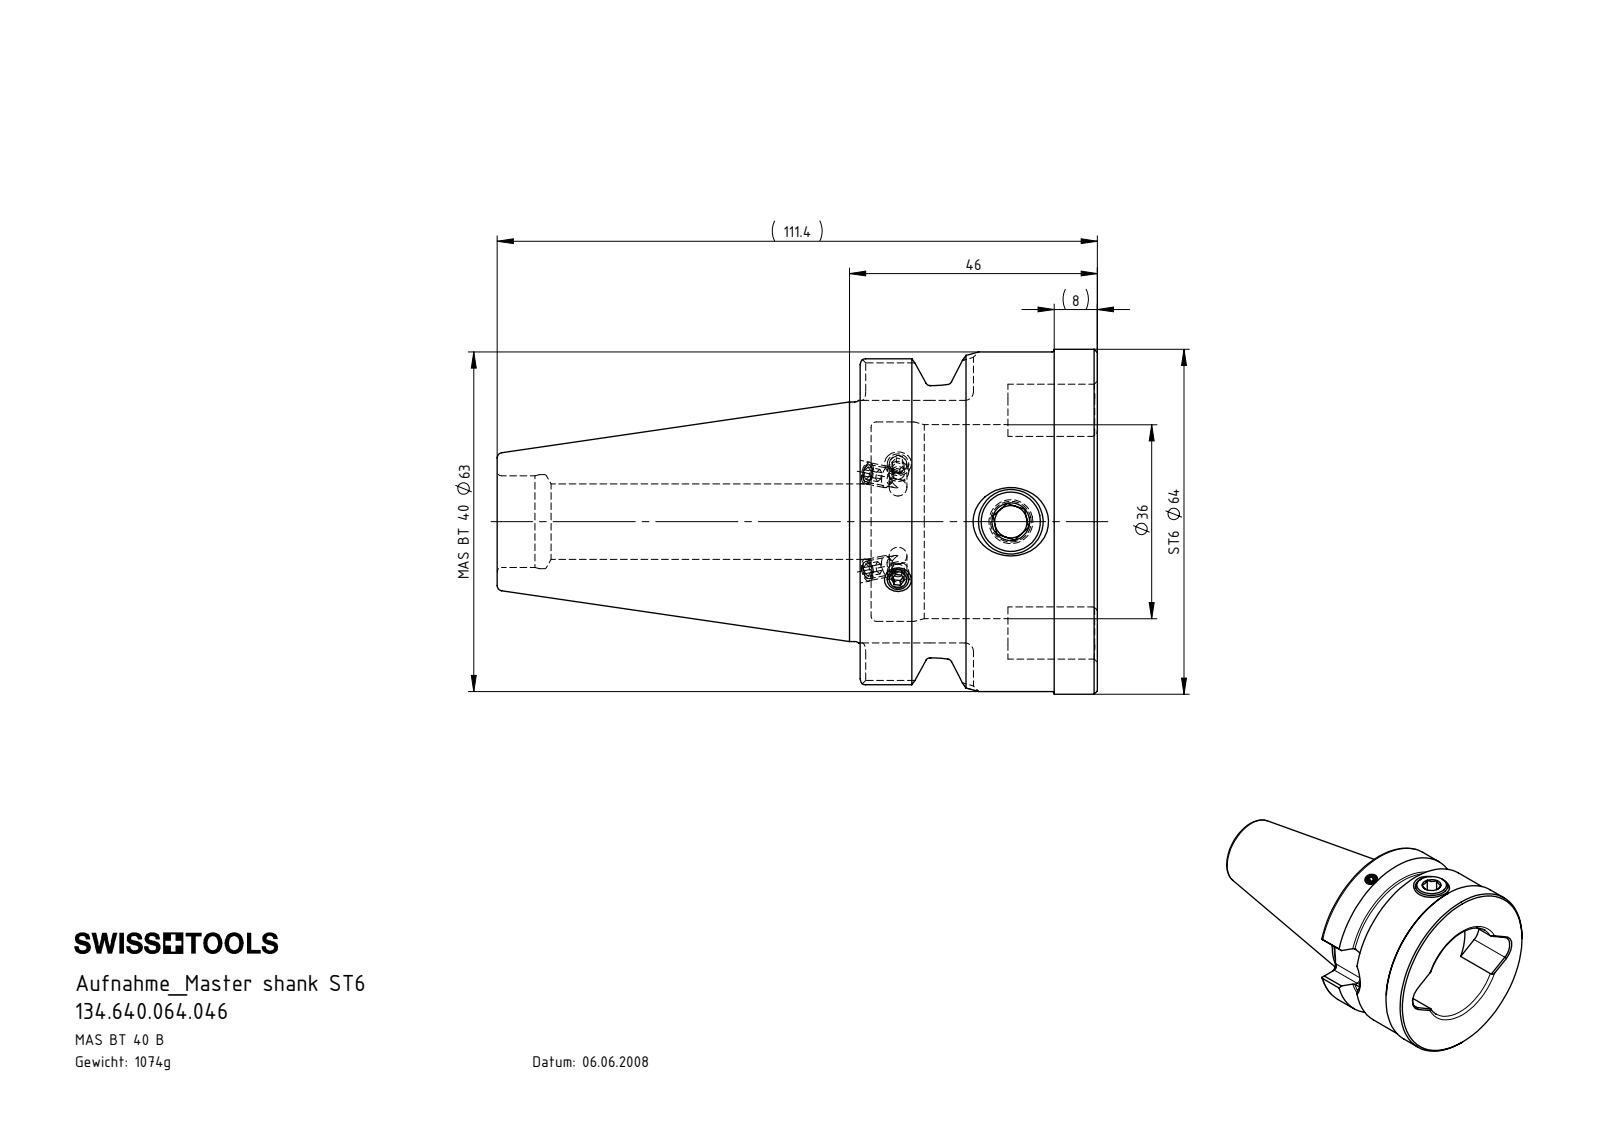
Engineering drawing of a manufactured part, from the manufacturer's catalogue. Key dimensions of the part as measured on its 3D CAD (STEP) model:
Part name (STEP PRODUCT): ST6-ER1.001.018_A; BB4-ST6.K01.046; BB4-ST6.K01.046_A_mit Bundkhlung
STEP written by: SolidWorks 2015 (CONFIG_CONTROL_DESIGN)
Units: millimetres
Bodies: 2 solids, 135 faces (36 planar, 42 cylindrical, 57 other)
Overall size (bounding box): 111.4 × 64 × 64
Volume: 137 524 mm³ · Surface area: 32 220 mm²
Round holes (diameter × count): ⌀4 ×2, ⌀11 ×1, ⌀14 ×1, ⌀17 ×1, ⌀17.45 ×1, ⌀36 ×1, ⌀42 ×1
Round bosses / shafts (diameter × count): ⌀64 ×1, ⌀63 ×1, ⌀53 ×1, ⌀44.45 ×1, ⌀12 ×1
Partial cylindrical surfaces — rounded edges, fillets, slot ends (radius × count): R1.6 ×8, R5.2 ×2, R8.05 ×1
Main face-to-face distances: 40.5, 3.5, 44, 6, 30.7, 9.5, 34.5, 45, 27.4, 23.9
